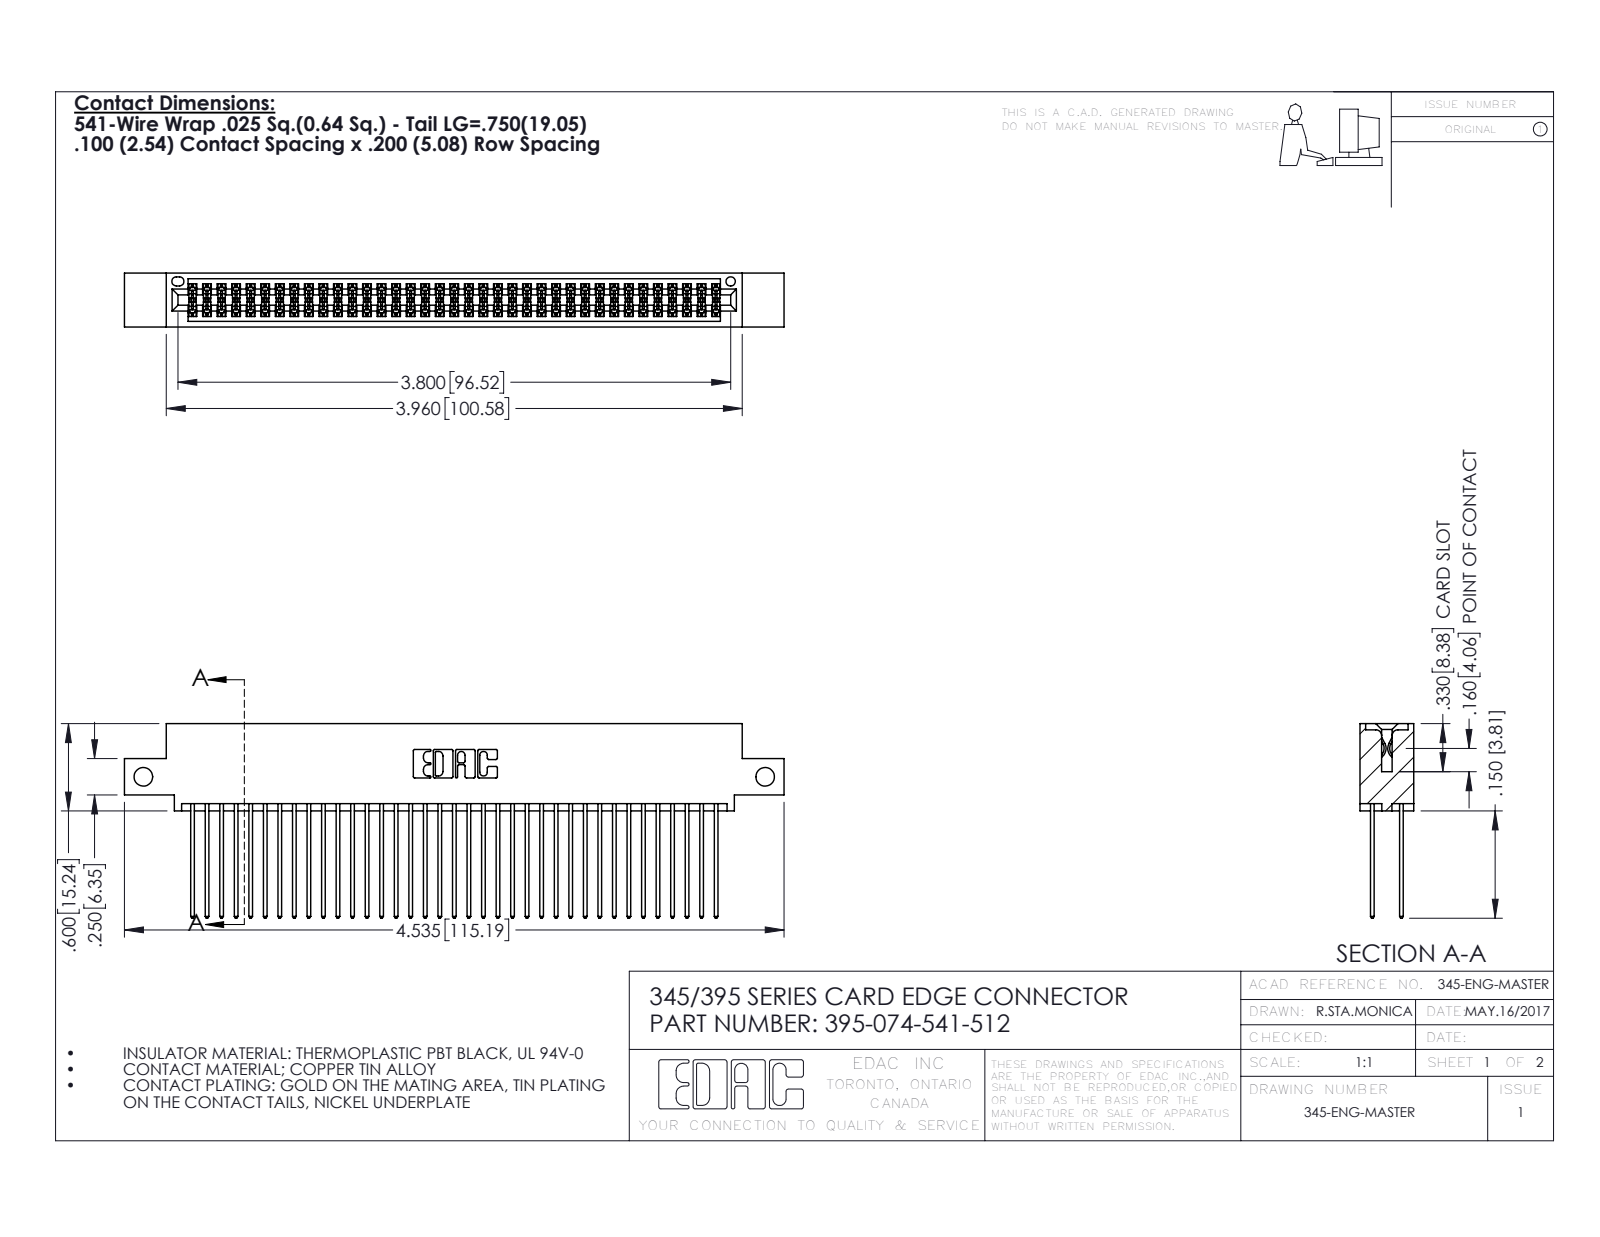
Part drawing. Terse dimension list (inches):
name: 345 Part_0.110 Offset - Side Mount; 395-074-541-512; 345-292-001_345-293-141
written by: SolidWorks 2016 (CONFIG_CONTROL_DESIGN)
unit: in
bodies: 75 solids, 3830 faces (2526 planar, 1304 cylindrical, 0 other)
size: 4.535 × 1.337 × 0.37
volume: 0.696 in³; area: 29.01 in²
holes: 2× ⌀0.128, 1× ⌀0.064
rounds: 111× R0.006, 74× R0.01, 22× R0.01, 6× R0.007, 6× R0.031, 3× R0.026, 2× R0.014, 2× R0.019
face distances: 0.298, 0.072, 0.2, 0.098, 0.272, 0.025, 0.225, 0.37, 0.175, 0.149
hole spacings: 4.275
